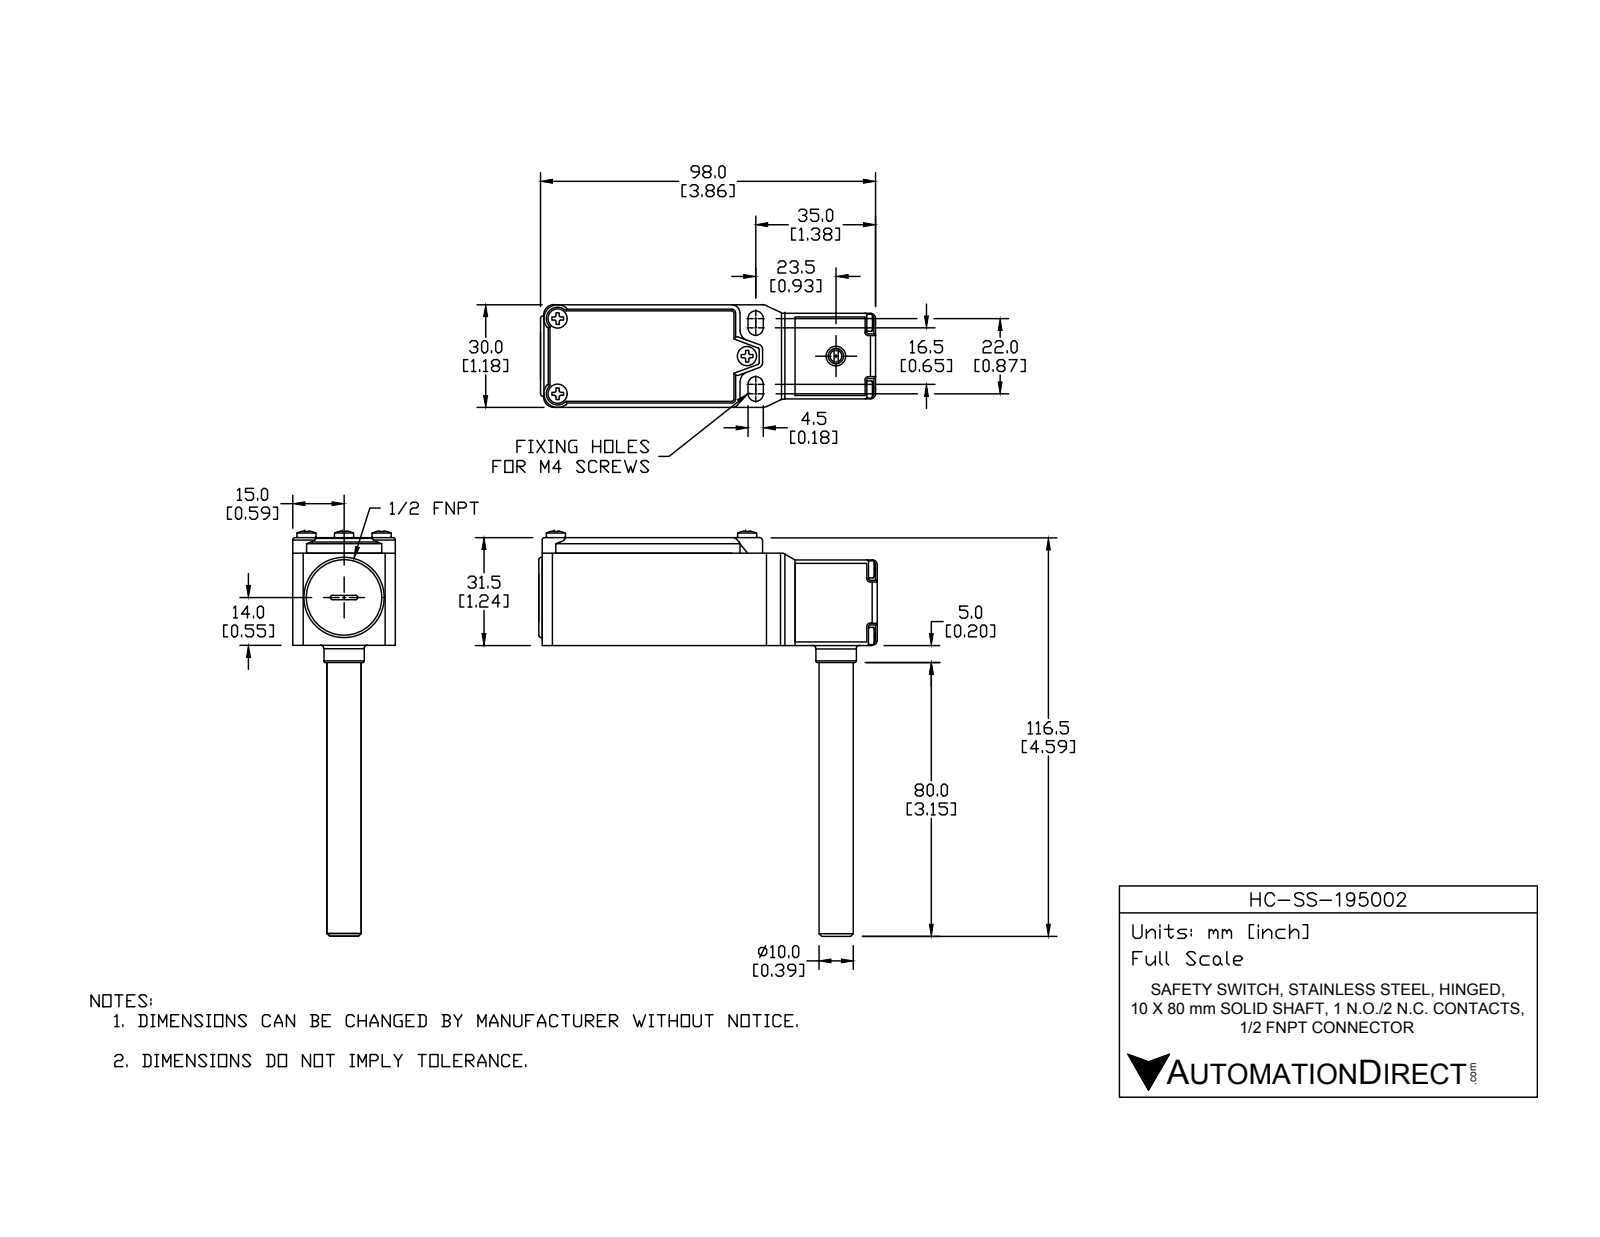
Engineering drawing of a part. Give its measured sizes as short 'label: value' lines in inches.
name: HC-SS-195002
written by: SolidWorks 2014 (AUTOMOTIVE_DESIGN)
unit: in
bodies: 13 solids, 1168 faces (347 planar, 466 cylindrical, 355 other)
size: 4.663 × 3.898 × 1.181
volume: 2.792 in³; area: 54.45 in²
holes: 8× ⌀0.098, 7× ⌀0.126, 3× ⌀0.157, 2× ⌀0.059, 2× ⌀0.071, 2× ⌀0.087, 2× ⌀0.142, 1× ⌀0.081, 1× ⌀0.114, 1× ⌀0.173, 1× ⌀0.185, 1× ⌀0.217
bosses: 7× ⌀0.118, 5× ⌀0.197, 4× ⌀0.138, 3× ⌀0.22, 1× ⌀0.925, 1× ⌀0.697, 1× ⌀0.394, 1× ⌀0.386
rounds: 175× R0.02, 20× R0.039, 18× R0.012, 14× R0.006, 8× R0.028, 8× R0.118, 6× R0.059, 4× R0.089
face distances: 0.098, 1.142, 0.079, 0.114, 1.067, 1.181, 0.177, 1.24, 0.016, 1.083
hole spacings: 0.543, 0.768, 0.187, 0.245, 0.414, 0.423, 0.426, 0.476
